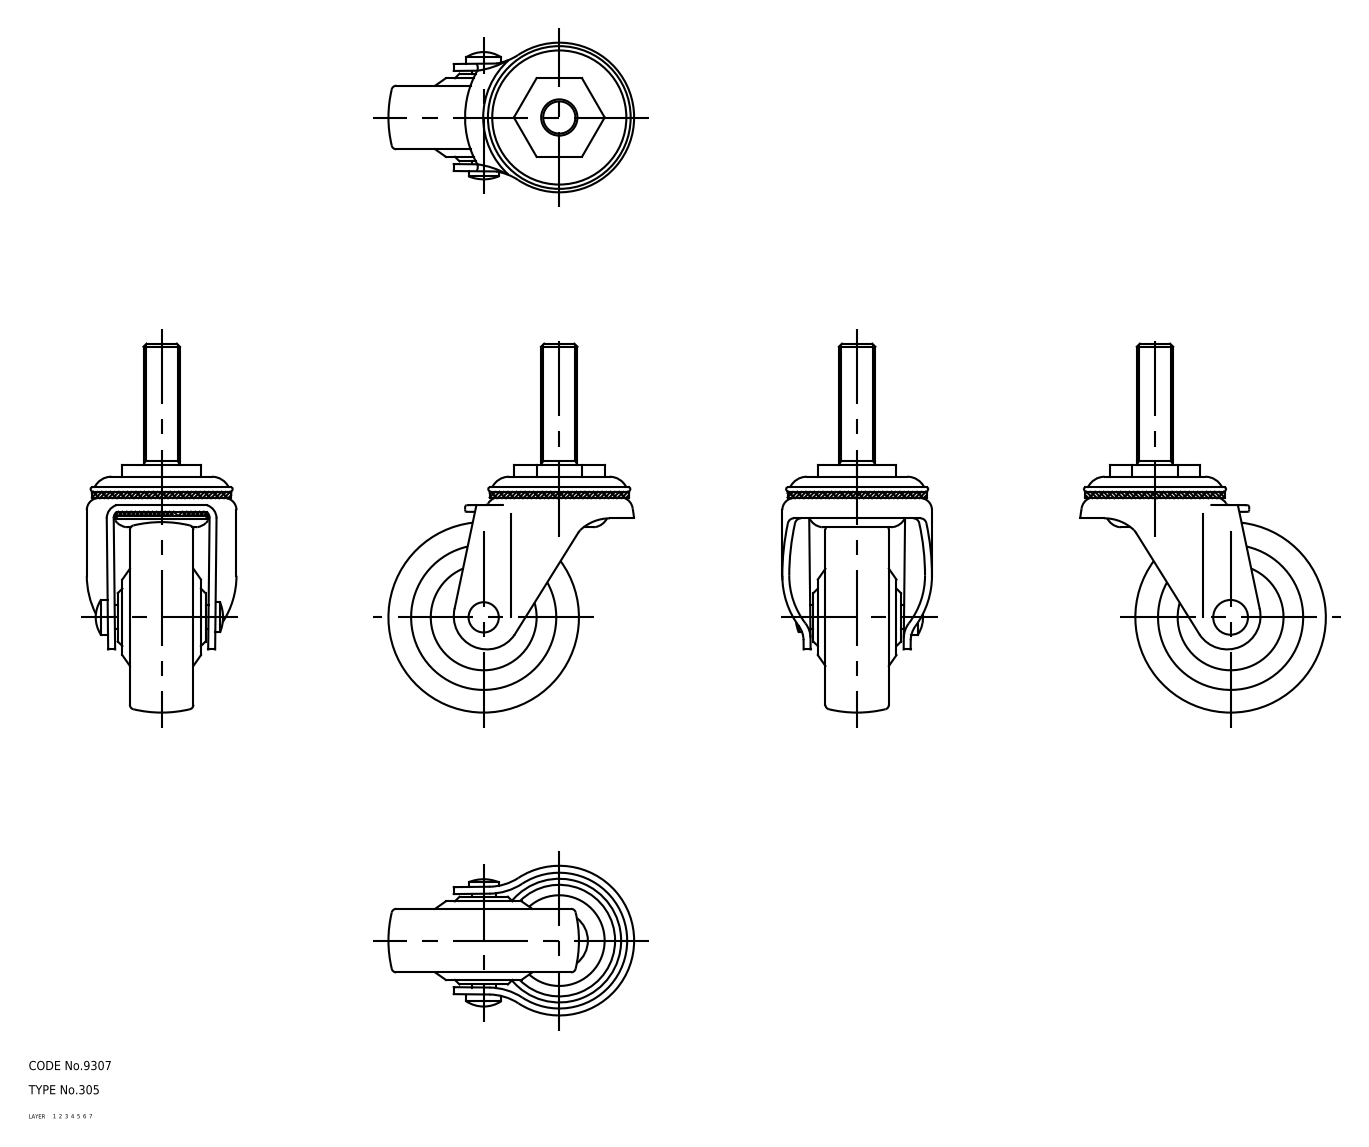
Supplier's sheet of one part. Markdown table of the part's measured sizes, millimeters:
| quantity | value |
| --- | --- |
| part name | axle; wheel; main shaft; No_305_23564_36 |
| STEP written by | CADfix (AUTOMOTIVE_DESIGN) |
| units | millimeters |
| bodies | 4 solids, 190 faces (0 planar, 0 cylindrical, 190 other) |
| overall size | 122 × 81.25 × 49.5 |
| volume | 98 920 mm³ |
| surface area | 29 588 mm² |
